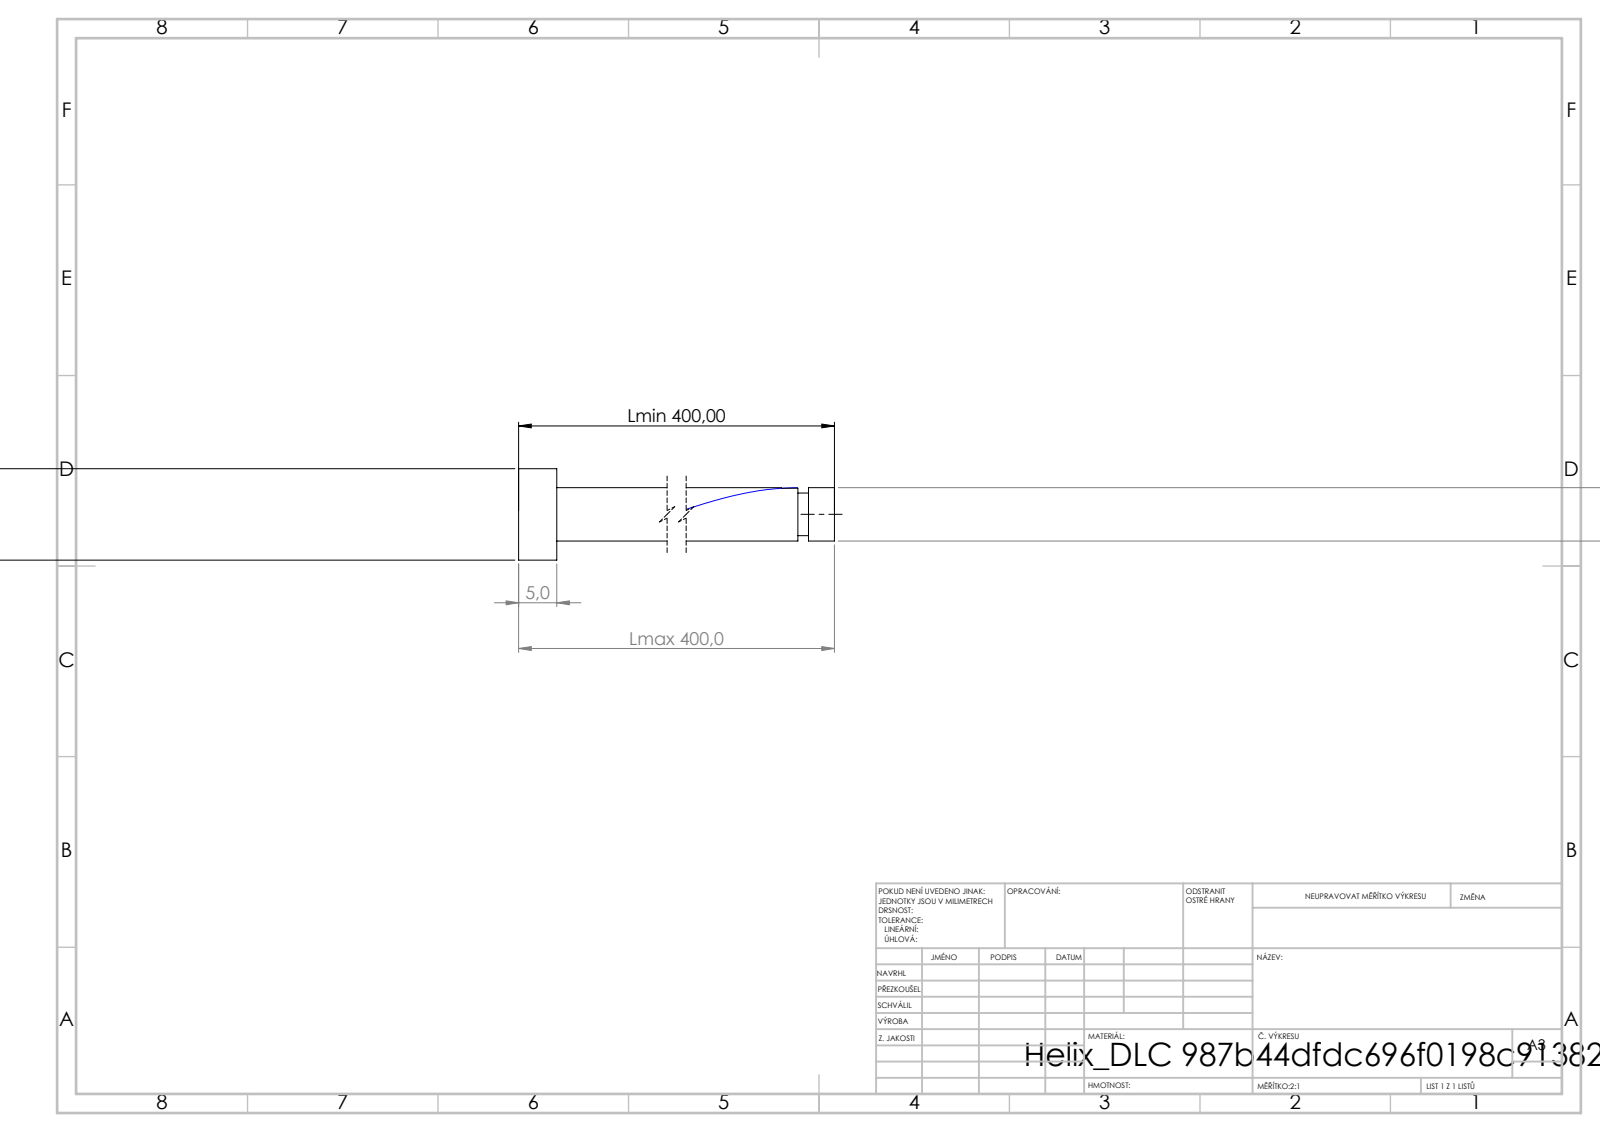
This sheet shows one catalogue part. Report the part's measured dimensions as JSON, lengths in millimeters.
{"step_written_by": "SolidWorks 2019 (CONFIG_CONTROL_DESIGN)", "units": "millimeters", "bodies": {"solids": 1, "faces": 16, "planar": 6, "cylindrical": 9, "other": 1}, "overall_size": [400, 12, 12], "volume_mm3": 19023, "surface_area_mm2": 12198, "round_bosses_or_shafts": [[12, 1], [7, 1], [5.6, 1]], "face_to_face_distances": [5, 400, 395, 396.59, 391.59, 3.41, 395.19, 390.19, 1.4, 4.81]}
